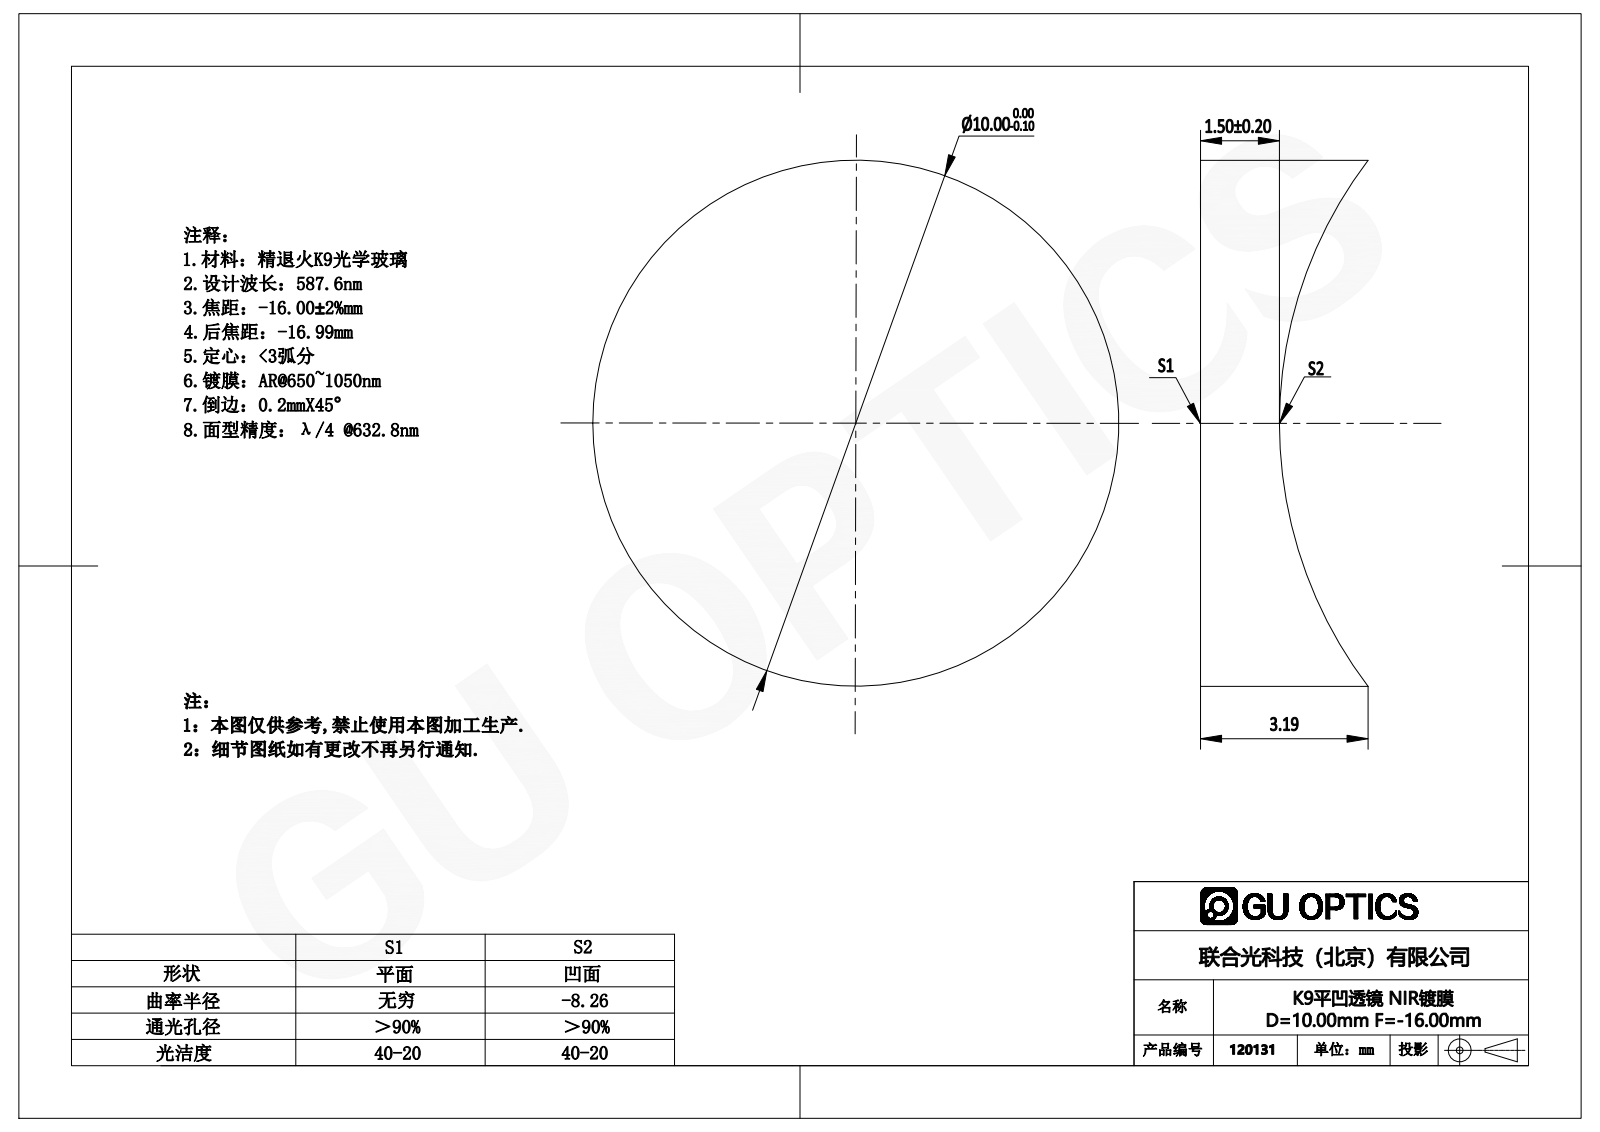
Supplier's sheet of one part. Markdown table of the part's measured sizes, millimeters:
| quantity | value |
| --- | --- |
| part name | 120131 |
| STEP written by | SolidWorks 2016 (AUTOMOTIVE_DESIGN) |
| units | millimeters |
| bodies | 1 solid, 5 faces (1 planar, 2 cylindrical, 2 other) |
| overall size | 10 × 10 × 3.19 |
| volume | 181 mm³ |
| surface area | 266 mm² |
| round bosses / shafts (diameter × count) | 10 × 1 |
